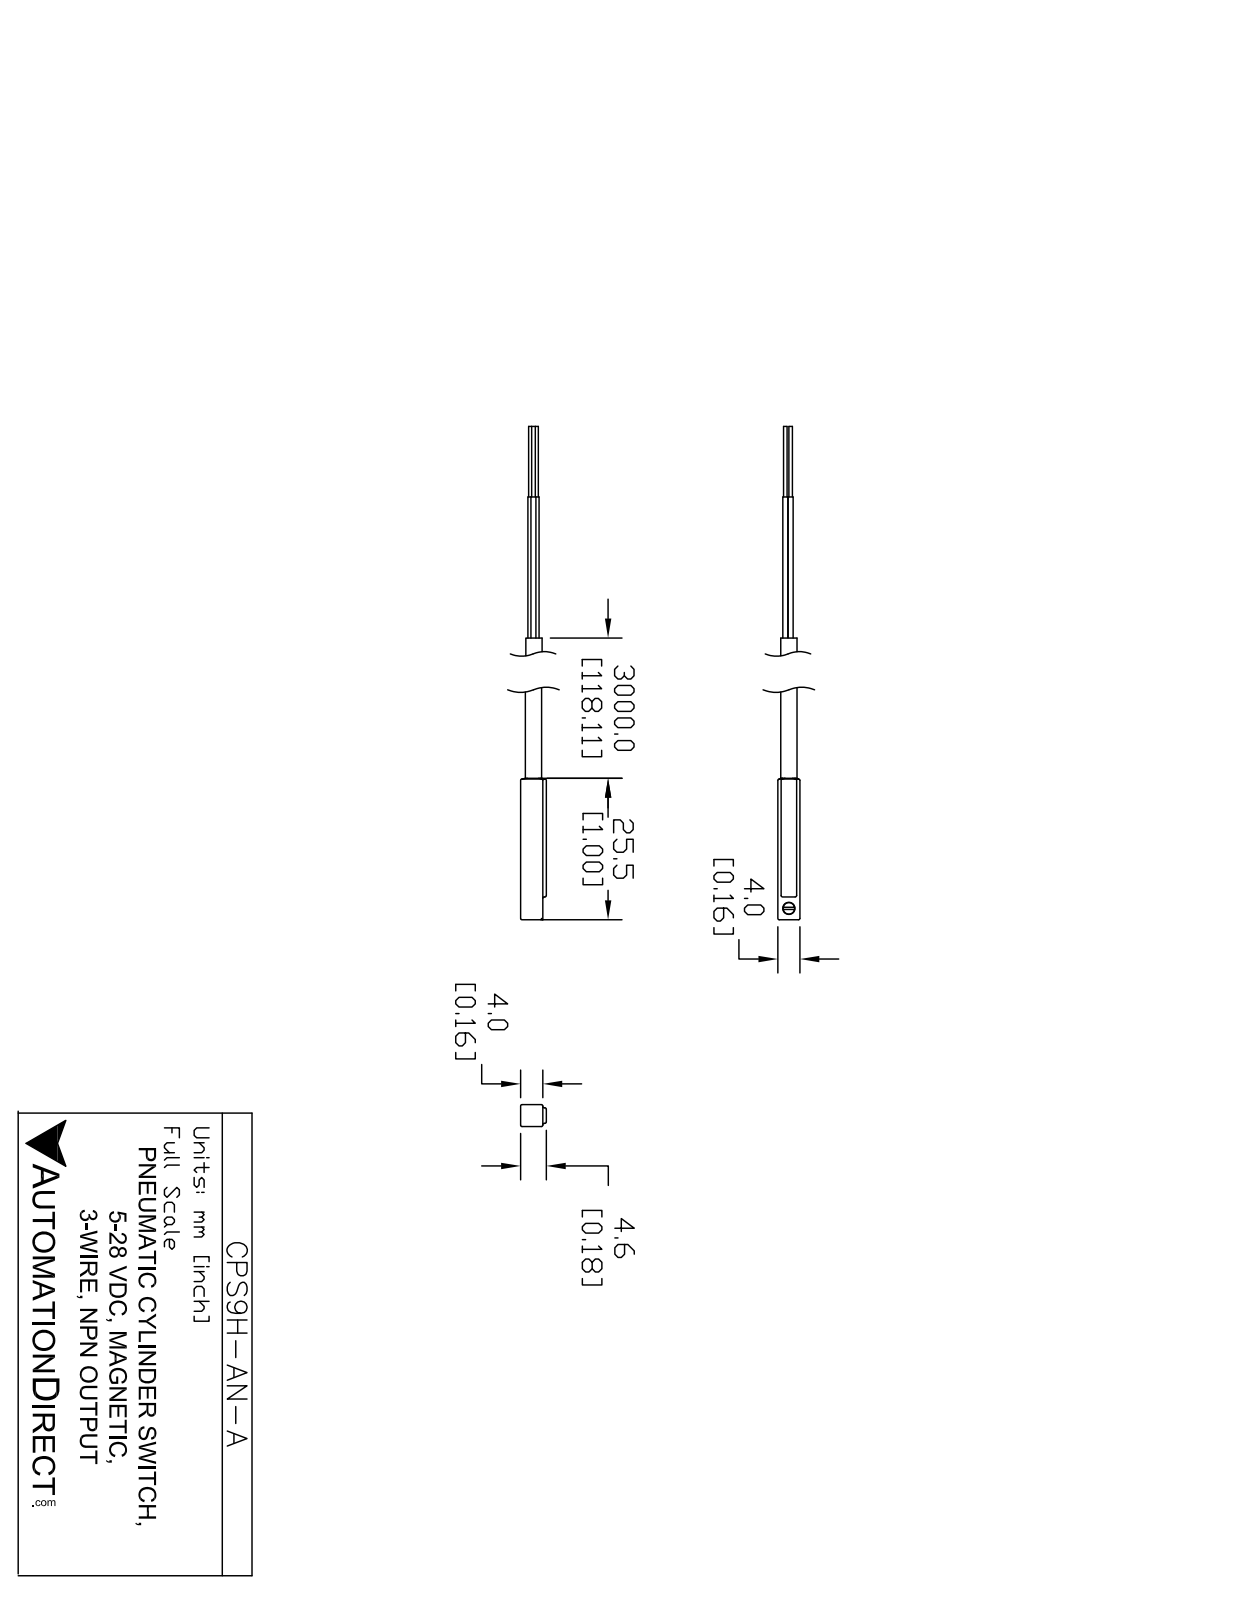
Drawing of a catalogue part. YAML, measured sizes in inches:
part_name: "9H72-000-031SW.igs2_1; CPS9H-AN-A; 9H72-000-031SW.igs1_1"
step_written_by: "SolidWorks 2014 (AUTOMOTIVE_DESIGN)"
units: inches
bodies: {solids: 2, faces: 97, planar: 22, cylindrical: 41, other: 34}
overall_size: [6.498, 0.182, 0.156]
volume: 0.072
surface_area: 2.663
round_holes:
  - {diameter: 0.086, count: 1}
round_bosses_or_shafts:
  - {diameter: 0.035, count: 3}
  - {diameter: 0.025, count: 3}
  - {diameter: 0.115, count: 1}
  - {diameter: 0.082, count: 1}
partial_cylinders:
  - {radius: 0.01, count: 22}
face_to_face_distances: [0.156, 0.182, 0.157, 0.025, 0.023, 0.133, 4.998, 0.11, 0.015, 1.5]
